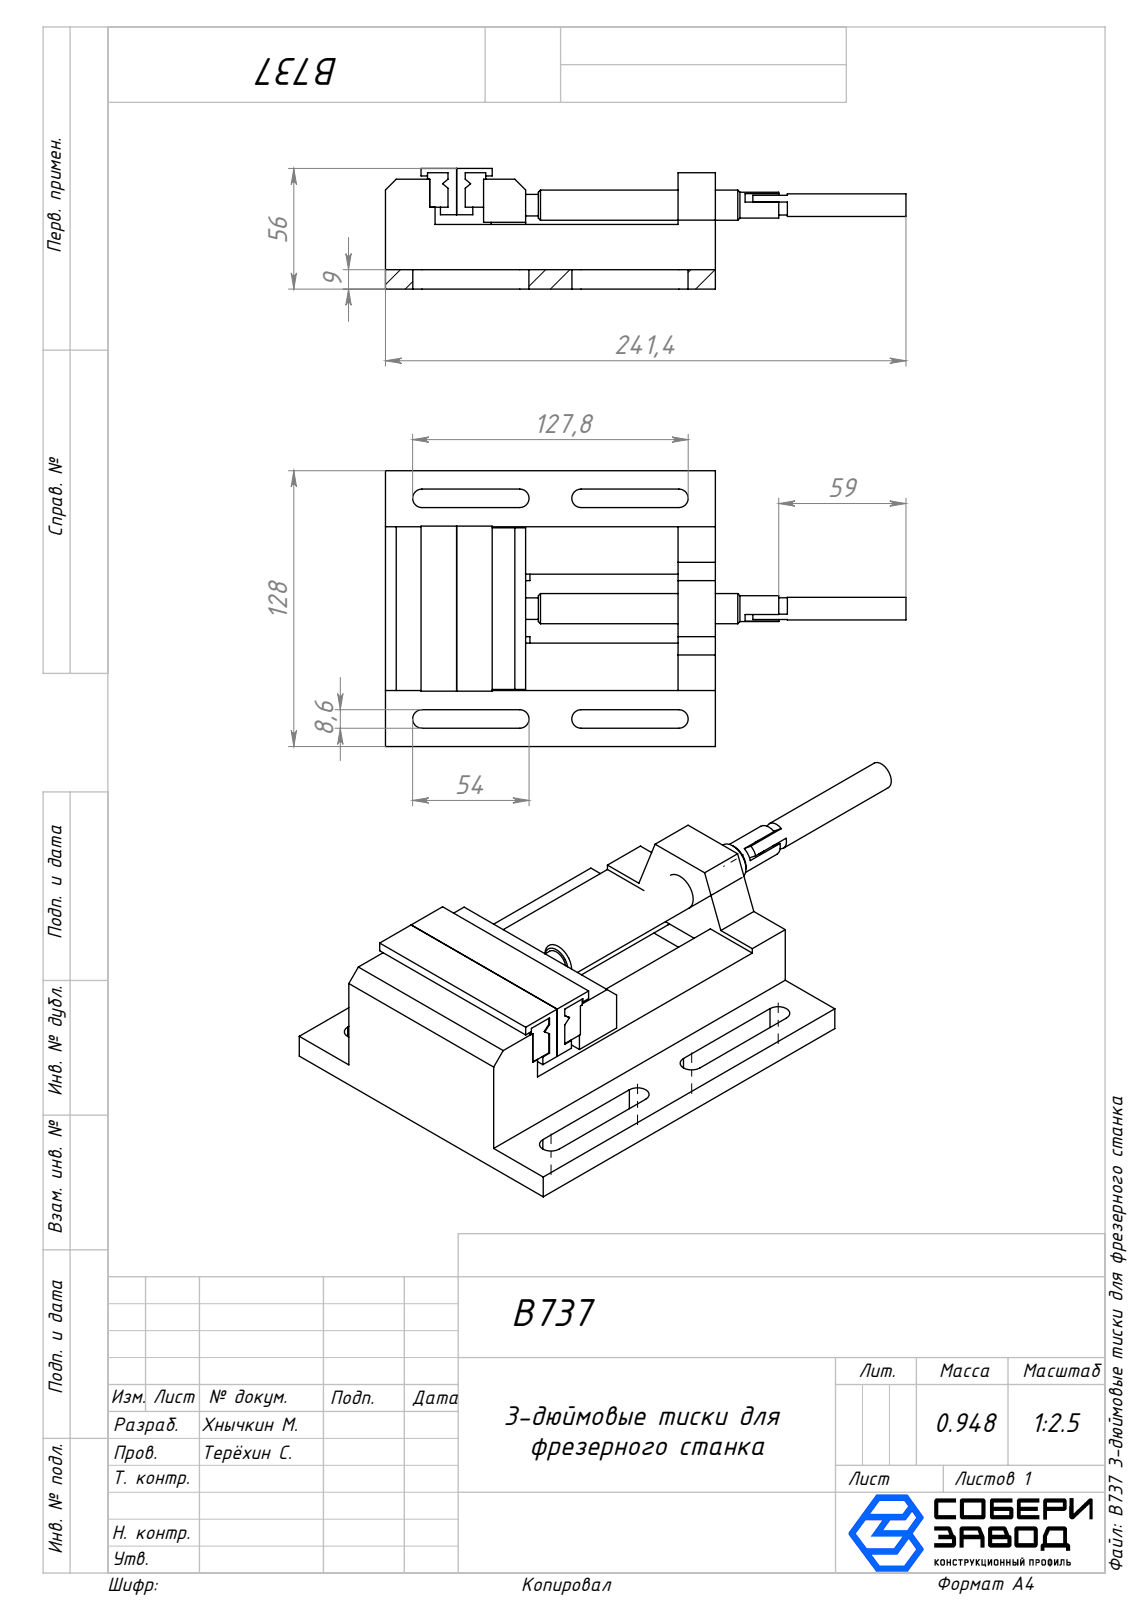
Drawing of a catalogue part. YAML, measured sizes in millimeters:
part_name: "B737 Ползун_00; B737 Ручка_00; Резина_00; Пластина_00 (+3 more)"
step_written_by: "SolidWorks 2025 (AUTOMOTIVE_DESIGN)"
units: millimeters
bodies: {solids: 8, faces: 177, planar: 121, cylindrical: 48, other: 8}
overall_size: [241.4, 128, 56]
volume: 332345
surface_area: 120952
round_holes:
  - {diameter: 10, count: 2}
  - {diameter: 3, count: 1}
  - {diameter: 12, count: 1}
  - {diameter: 19.5, count: 1}
round_bosses_or_shafts:
  - {diameter: 20, count: 2}
  - {diameter: 14, count: 1}
  - {diameter: 10.5, count: 1}
  - {diameter: 10, count: 1}
  - {diameter: 6, count: 1}
partial_cylinders:
  - {radius: 4.3, count: 8}
  - {radius: 3, count: 6}
face_to_face_distances: [12.5, 2, 8.5, 21.5, 16.5, 21, 4, 30, 26, 9]
hole_center_spacings: [36.2, 46]
